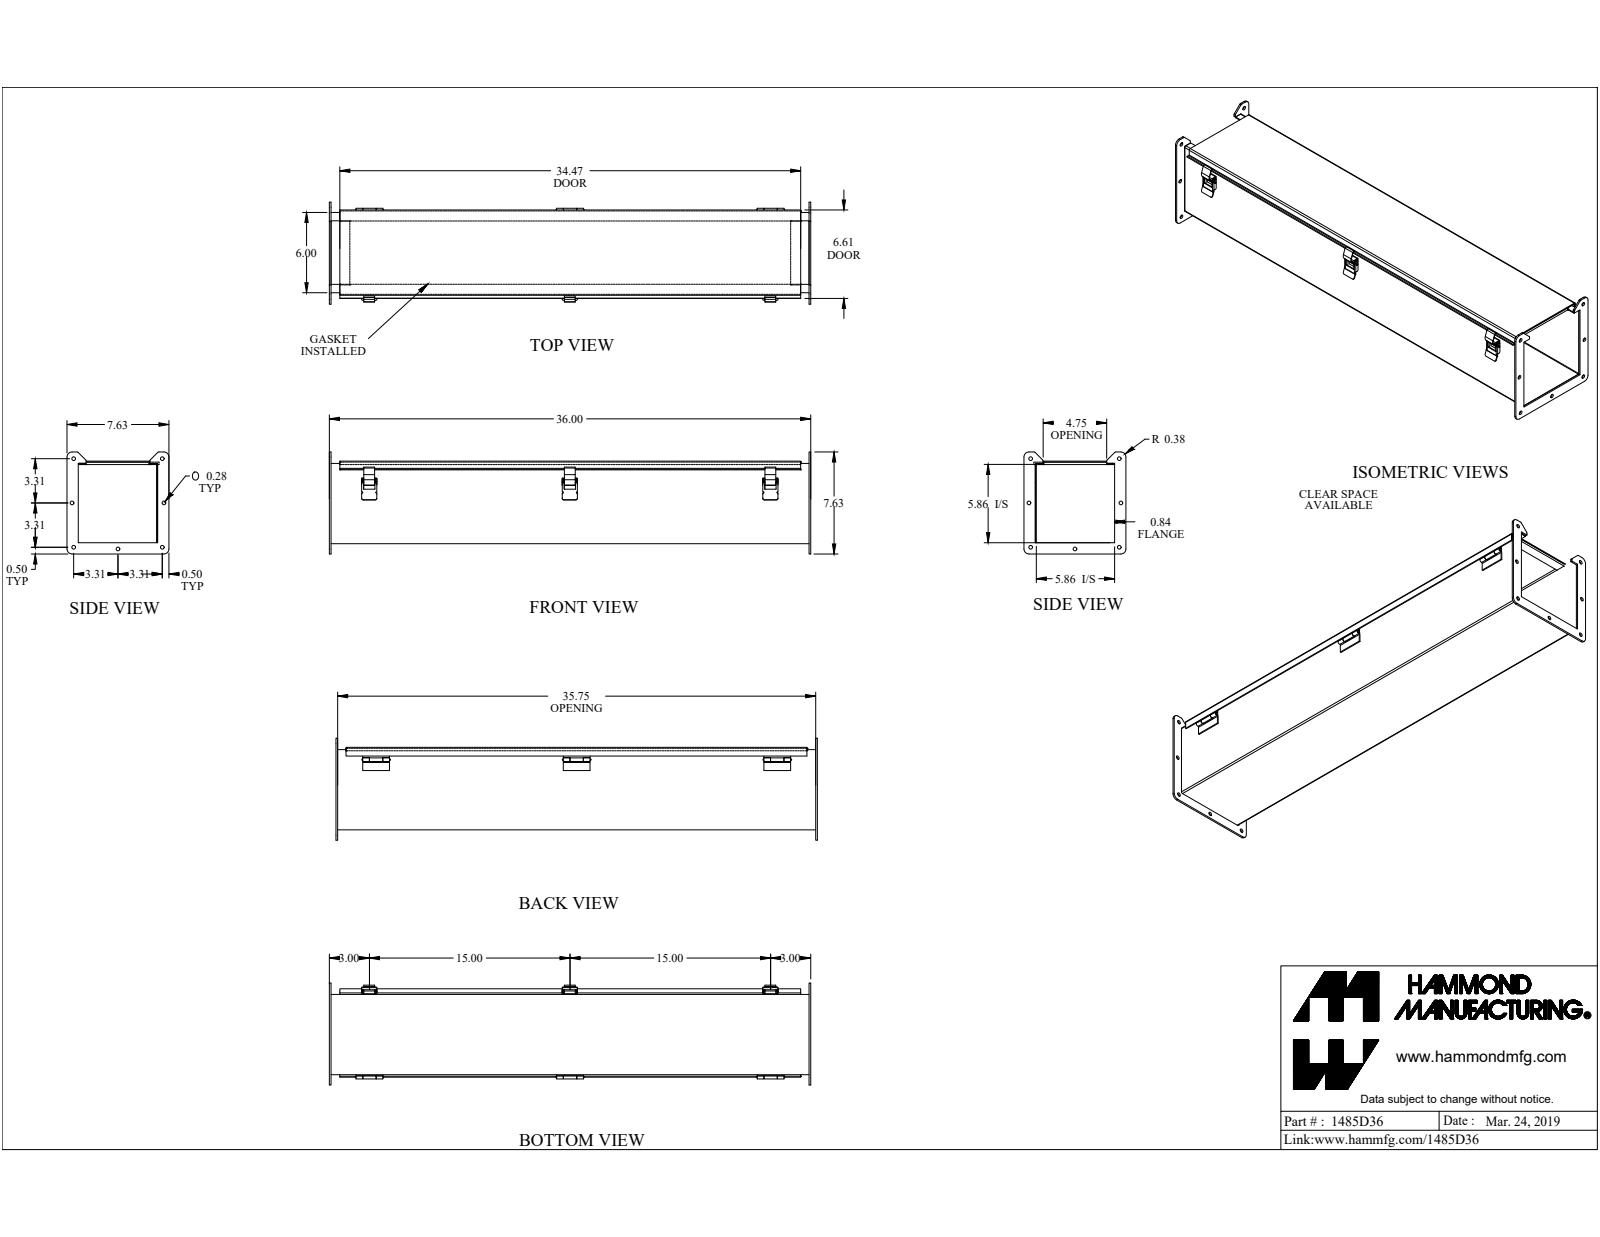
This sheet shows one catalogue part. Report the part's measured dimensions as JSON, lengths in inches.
{"part_name": "1485D36", "step_written_by": "SolidWorks 2019 (CONFIG_CONTROL_DESIGN)", "units": "inches", "bodies": {"solids": 26, "faces": 561, "planar": 334, "cylindrical": 221, "other": 6}, "overall_size": [36, 7.625, 7.625], "volume_in3": 84.76, "surface_area_in2": 2183, "round_holes": [[0.281, 7], [0.125, 1], [0.13, 1], [0.164, 1]], "round_bosses_or_shafts": [[0.187, 2], [0.275, 1], [0.156, 1], [0.125, 1], [0.125, 1]], "partial_cylinders_radius": [[0.016, 19], [0.125, 11], [0.035, 7], [0.036, 7], [0.039, 7], [0.076, 7], [0.108, 7], [0.015, 6]], "face_to_face_distances": [0.072, 5.928, 6.1, 6, 5.856, 6.028, 6.172, 0.172, 5.913, 5.841], "hole_center_spacings": [7.519, 6.625, 3.315, 3.315, 9.369, 0.285, 1.112, 1.459]}
